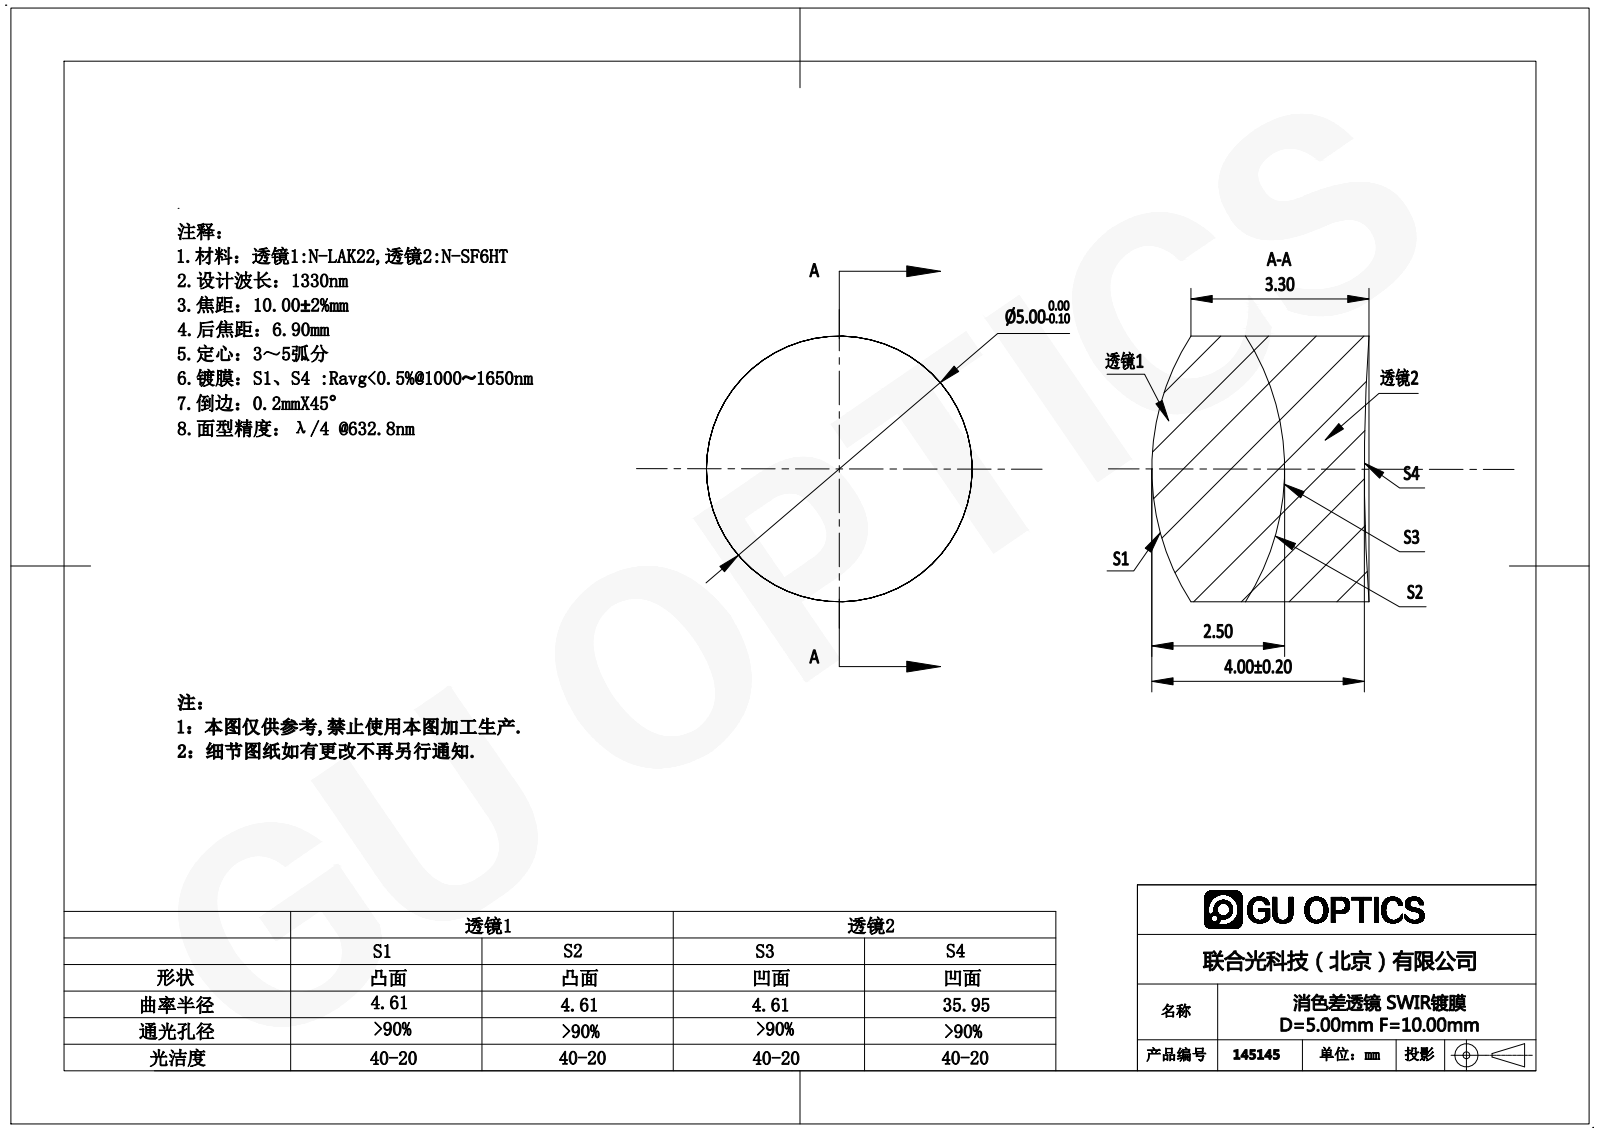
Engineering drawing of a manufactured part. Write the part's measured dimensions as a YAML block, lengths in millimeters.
part_name: "145145"
step_written_by: "SolidWorks 2016 (AUTOMOTIVE_DESIGN)"
units: millimeters
bodies: {solids: 2, faces: 12, planar: 0, cylindrical: 4, other: 8}
overall_size: [5, 5, 4.09]
volume: 72
surface_area: 136
round_bosses_or_shafts:
  - {diameter: 5, count: 1}
